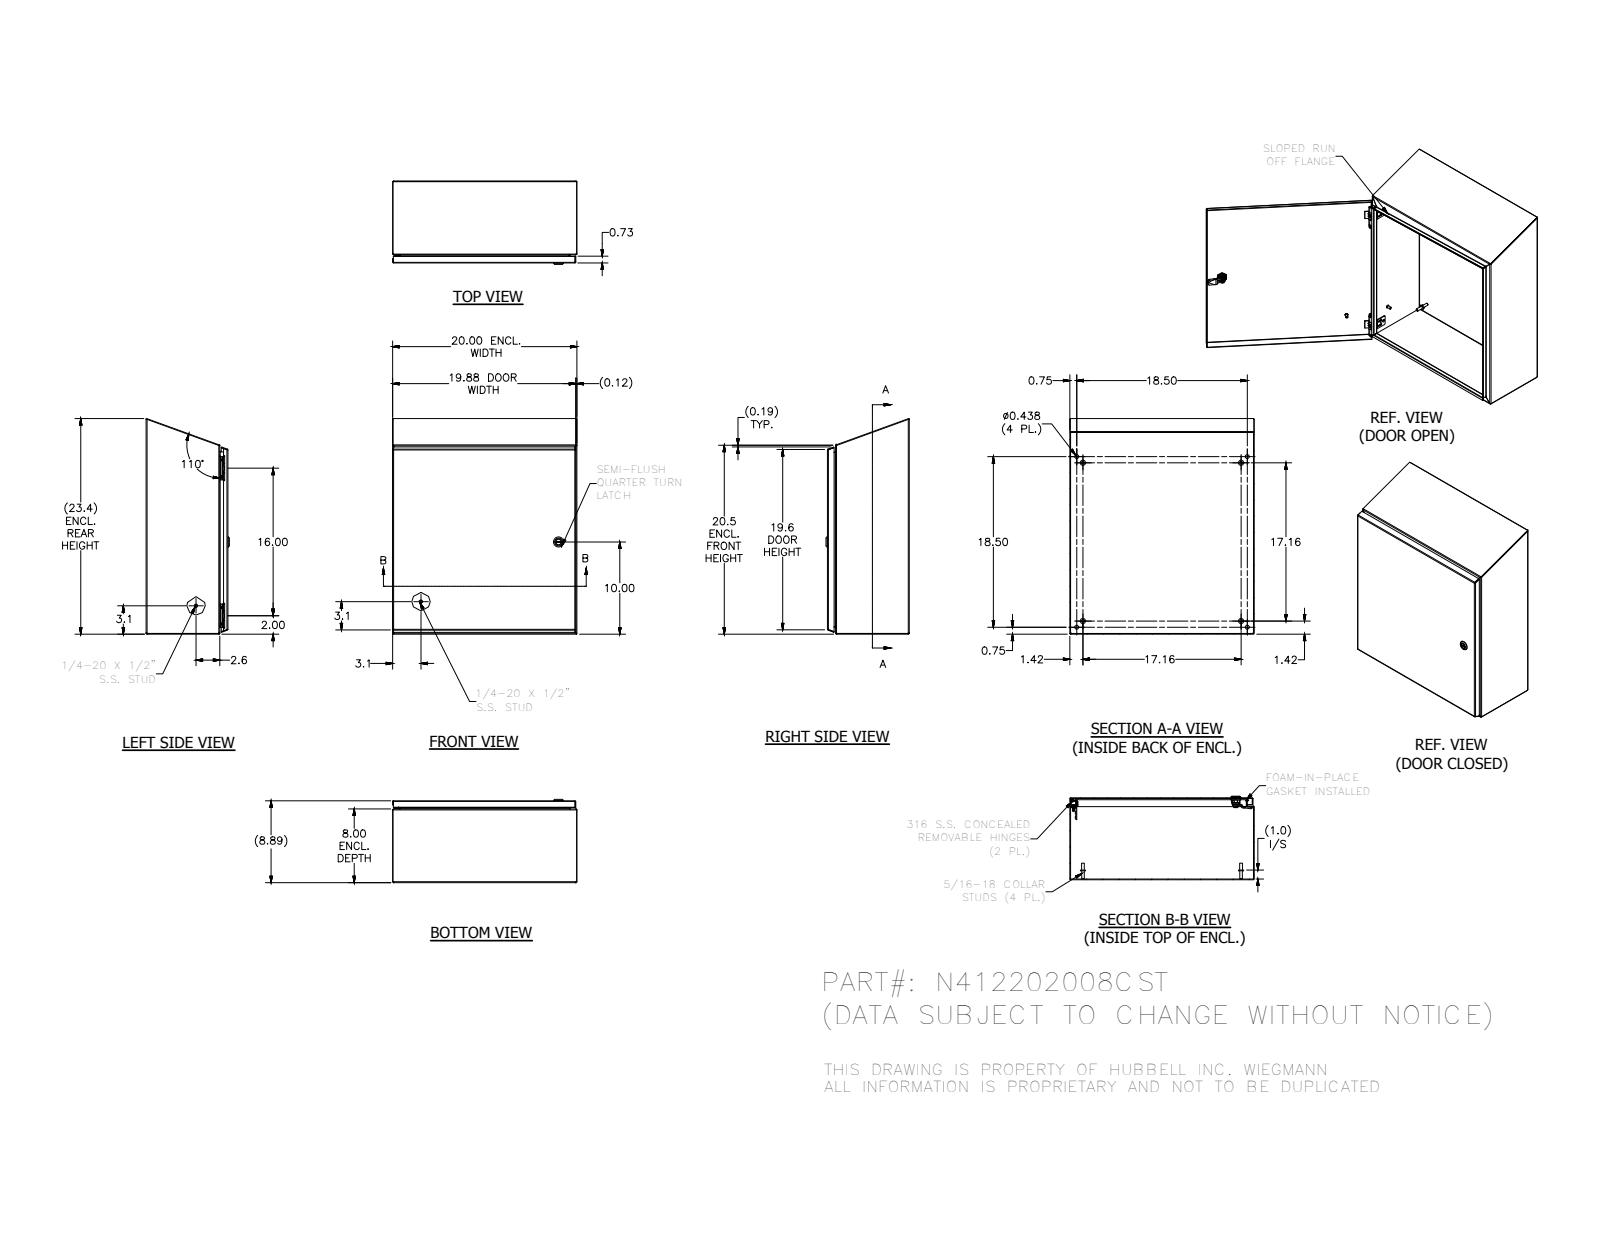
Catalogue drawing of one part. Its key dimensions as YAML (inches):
part_name: "N412202008CST"
step_written_by: "SolidWorks 2018 (AUTOMOTIVE_DESIGN)"
units: inches
bodies: {solids: 36, faces: 1521, planar: 568, cylindrical: 552, other: 401}
overall_size: [23.391, 20, 9.044]
volume: 127.4
surface_area: 3463
round_holes:
  - {diameter: 0.093, count: 4}
  - {diameter: 0.152, count: 4}
  - {diameter: 0.167, count: 4}
  - {diameter: 0.172, count: 4}
  - {diameter: 0.187, count: 4}
  - {diameter: 0.437, count: 4}
  - {diameter: 0.156, count: 3}
  - {diameter: 0.187, count: 1}
  - {diameter: 0.197, count: 1}
  - {diameter: 0.315, count: 1}
  - {diameter: 0.394, count: 1}
  - {diameter: 0.402, count: 1}
round_bosses_or_shafts:
  - {diameter: 0.25, count: 10}
  - {diameter: 0.563, count: 4}
  - {diameter: 0.36, count: 4}
  - {diameter: 0.32, count: 4}
  - {diameter: 0.3, count: 4}
  - {diameter: 0.275, count: 4}
  - {diameter: 0.256, count: 4}
  - {diameter: 0.164, count: 4}
partial_cylinders:
  - {radius: 0.012, count: 30}
  - {radius: 0.031, count: 29}
  - {radius: 0.05, count: 26}
  - {radius: 0.105, count: 19}
  - {radius: 0.016, count: 18}
  - {radius: 0.125, count: 16}
  - {radius: 0.02, count: 13}
  - {radius: 0.032, count: 8}
face_to_face_distances: [0.074, 8.813, 8.739, 8.887, 19.926, 19.852, 20, 7.926, 0.887, 0.813]
hole_center_spacings: [16, 18.5, 18.872, 0.5, 0.656, 0.66, 0.984, 1.307]
